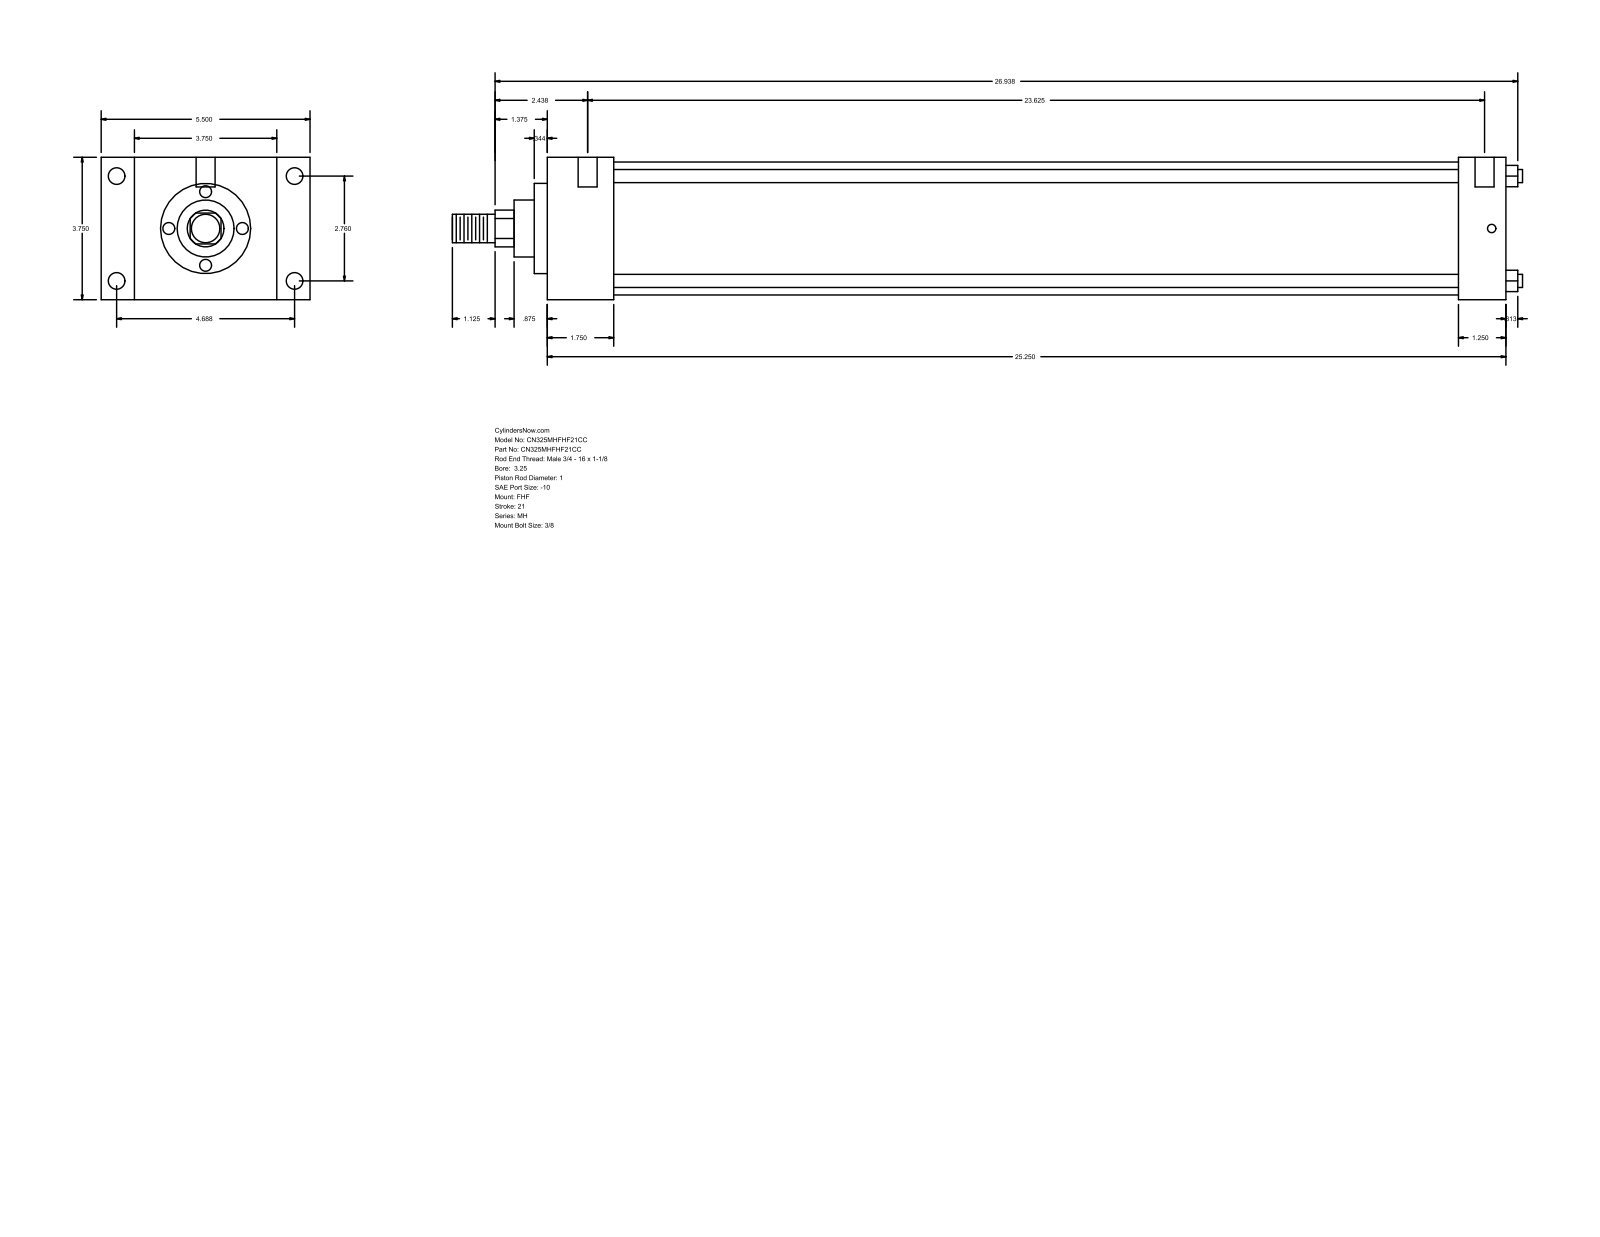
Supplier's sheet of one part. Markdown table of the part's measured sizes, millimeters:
| quantity | value |
| --- | --- |
| part name | MH_FHF__0325_1 |
| STEP written by | GSSL Pune (CONFIG_CONTROL_DESIGN) |
| units | millimeters |
| bodies | 0 solids, 90 faces (61 planar, 29 cylindrical, 0 other) |
| overall size | 715.96 × 139.7 × 95.25 |
| round holes (diameter × count) | 5.56 × 4, 11.13 × 4, 12.7 × 2 |
| round bosses / shafts (diameter × count) | 8.76 × 4, 88.9 × 1, 60.33 × 1, 38.1 × 1, 25.4 × 1, 19.05 × 1 |
| partial cylindrical surfaces (radius × count) | 12.29 × 1 |
| main face-to-face distances | 95.24, 641.35, 44.46, 596.89, 22.23, 117.47, 139.7, 609.6, 565.14, 31.75 |
| hole center spacings | 70.1, 119.06, 138.16, 606.42, 1.58, 4.76, 600.08, 601.66 |
